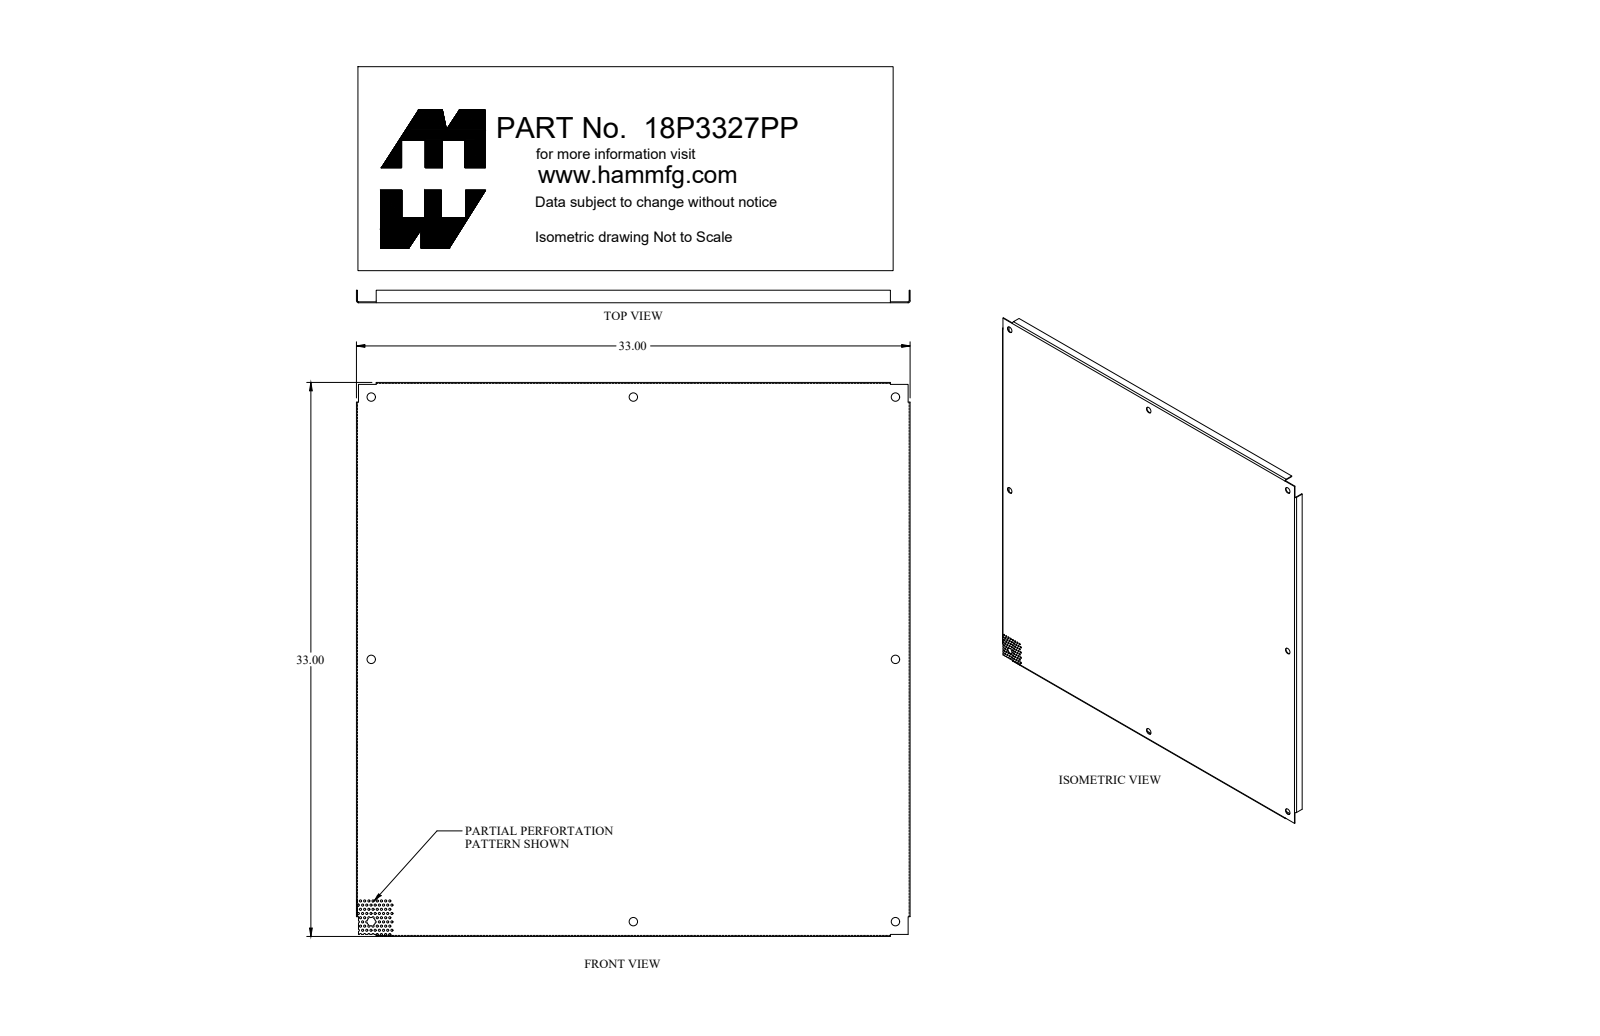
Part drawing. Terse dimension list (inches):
name: 18P3333PP_Default
written by: SolidWorks 2018 (CONFIG_CONTROL_DESIGN)
unit: in
bodies: 1 solid, 262 faces (43 planar, 211 cylindrical, 8 other)
size: 33 × 33 × 0.75
volume: 66.54 in³; area: 2 345 in²
holes: 74× ⌀0.125, 7× ⌀0.5
rounds: 17× R0.063, 8× R0.062, 4× R0.029, 4× R0.086, 1× R0.25
face distances: 0.057, 32.943, 32.886, 33, 0.75, 0.693, 0.102, 32.898, 0.045, 32.841
hole spacings: 0.28, 0.5, 0.25, 0.451, 0.559, 0.673, 0.75, 0.76
